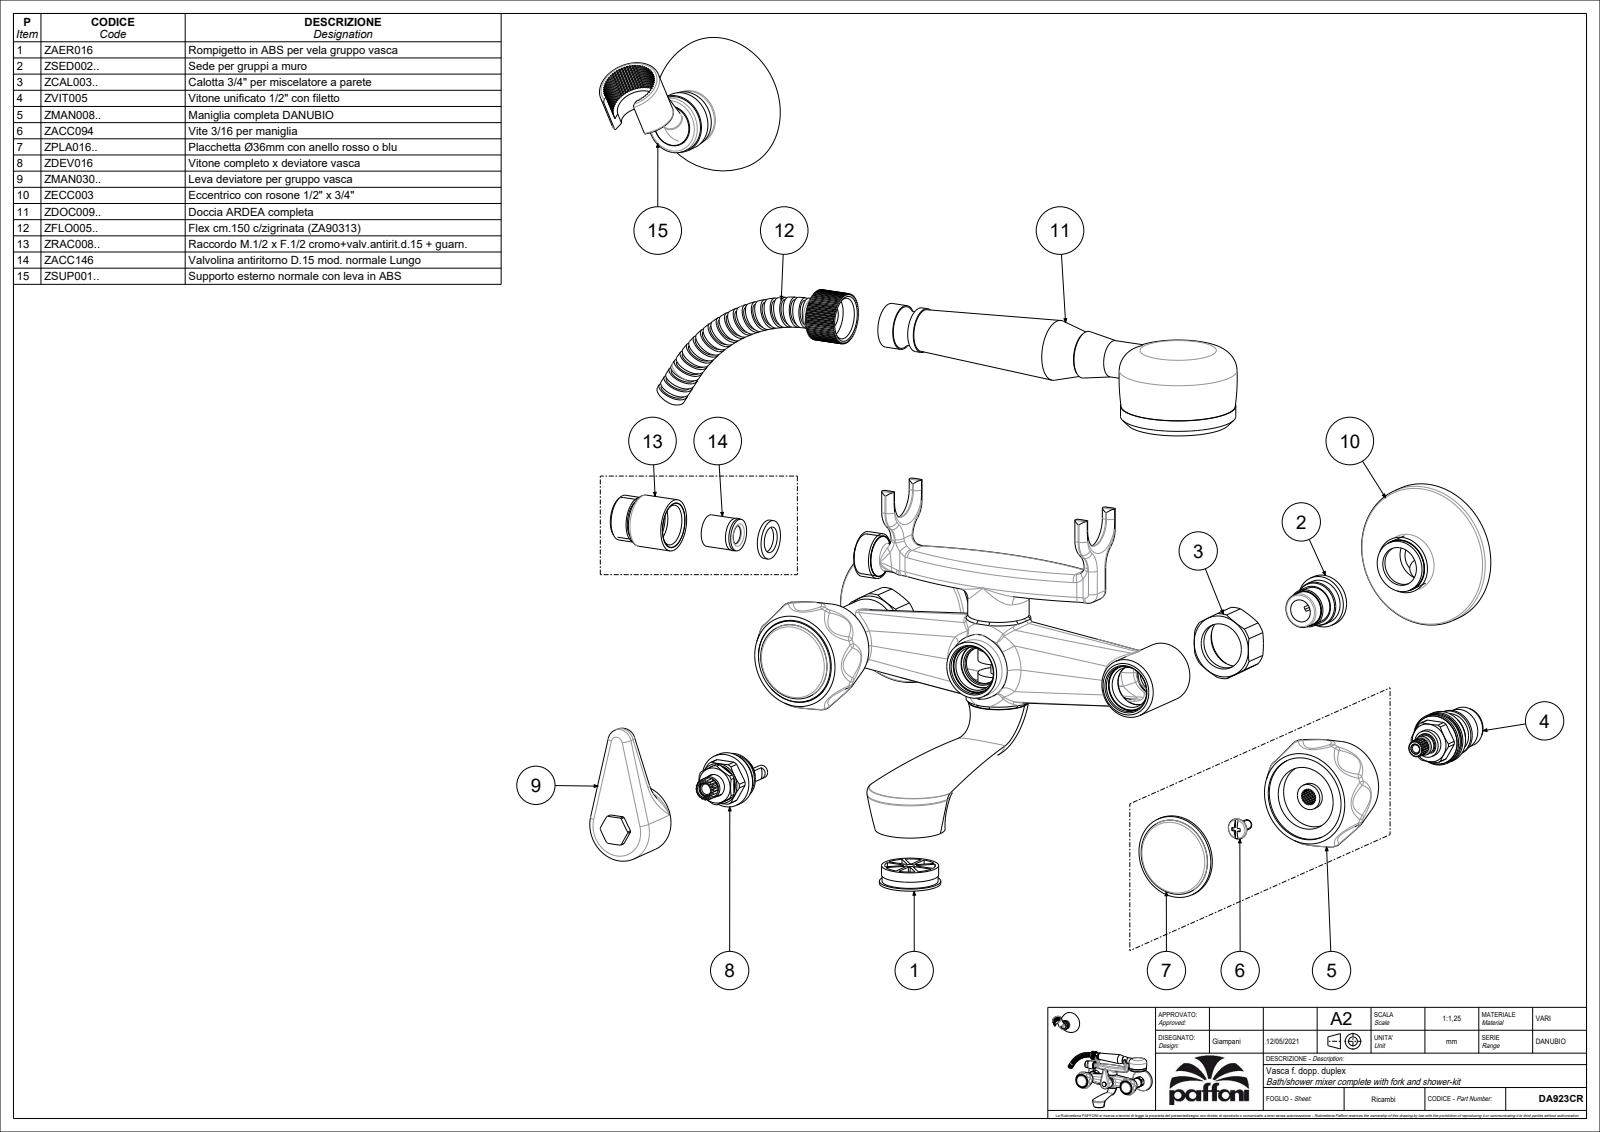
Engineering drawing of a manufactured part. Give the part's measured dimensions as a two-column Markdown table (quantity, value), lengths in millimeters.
| quantity | value |
| --- | --- |
| part name | DA923CR |
| STEP written by | CREO PARAMETRIC BY PTC INC, 2020044 (CONFIG_CONTROL_DESIGN) |
| units | millimeters |
| bodies | 5 solids, 2047 faces (767 planar, 672 cylindrical, 608 other) |
| overall size | 350.21 × 250.66 × 155 |
| volume | 489 732 mm³ |
| surface area | 177 659 mm² |
| round holes (diameter × count) | 1 × 108, 10.5 × 3, 18 × 3, 25 × 3, 21.5 × 2, 23.5 × 2, 24.1 × 2, 26.7 × 2, 35.8 × 2, 39 × 2, 65.4 × 2, 4 × 1 |
| round bosses / shafts (diameter × count) | 20.5 × 4, 24 × 3, 66 × 2, 38.5 × 2, 30.5 × 2, 28.5 × 2, 27.5 × 2, 25.6 × 2 |
| partial cylindrical surfaces (radius × count) | 1 × 28, 3 × 25, 21.31 × 16, 10 × 9, 5 × 6, 1.5 × 4, 6 × 3, 15.5 × 3 |
| main face-to-face distances | 1, 12, 13, 29, 9.5, 7.5, 6.6, 23.8, 35.3, 2.8 |
| hole center spacings | 8.21, 2.09, 21.75, 4.17, 22.55, 16.97, 19.66, 20.78 |
